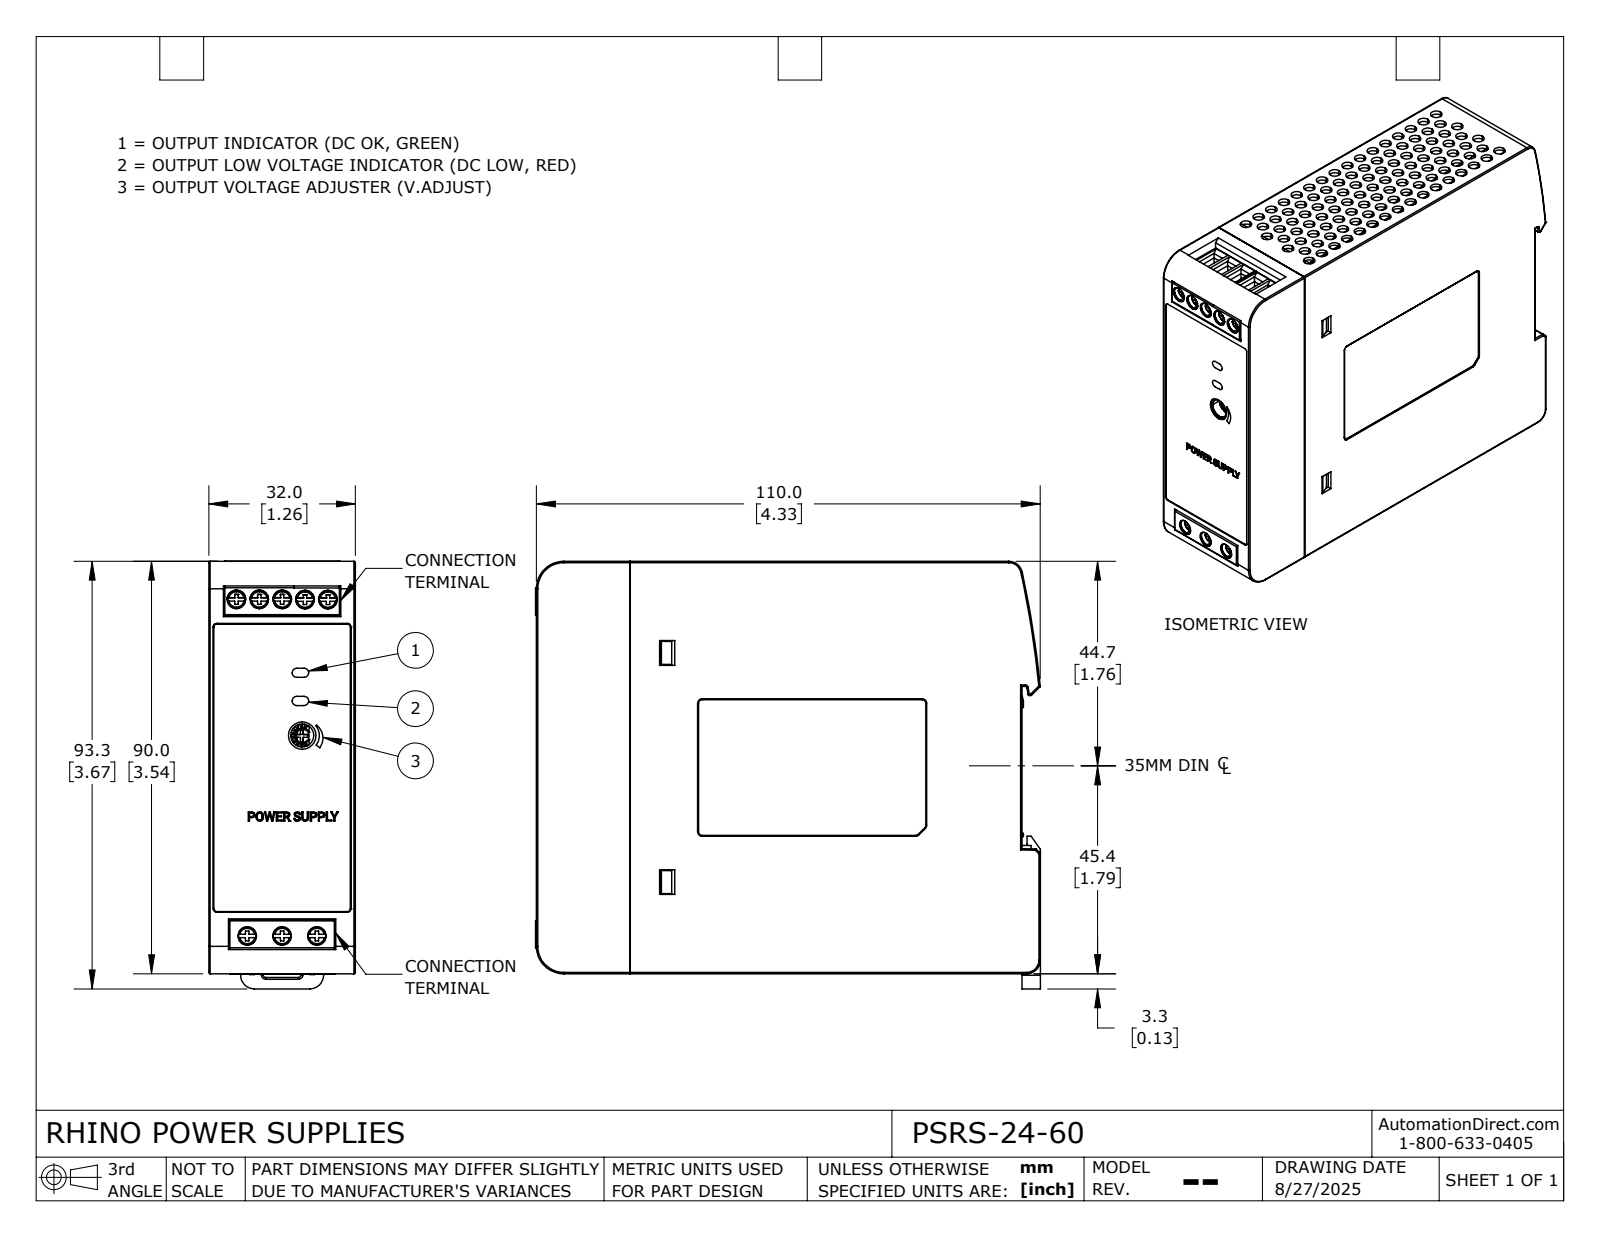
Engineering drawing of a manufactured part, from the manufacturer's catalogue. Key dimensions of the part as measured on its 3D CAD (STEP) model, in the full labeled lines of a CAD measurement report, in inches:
Part name (STEP PRODUCT): PSRS-24-60
STEP written by: SolidWorks 2024 (AUTOMOTIVE_DESIGN)
Units: inches
Bodies: 1 solid, 1700 faces (913 planar, 192 cylindrical, 595 other)
Overall size (bounding box): 4.339 × 3.673 × 1.26
Volume: 18.61 in³ · Surface area: 60.8 in²
Round holes (diameter × count): ⌀0.15 ×8, ⌀0.159 ×8, ⌀0.134 ×1, ⌀0.197 ×1
Round bosses / shafts (diameter × count): ⌀0.156 ×8, ⌀0.118 ×1
Partial cylindrical surfaces — rounded edges, fillets, slot ends (radius × count): R0.012 ×49, R0.039 ×12, R0.004 ×10, R0.02 ×7, R0.118 ×4, R0.098 ×3, R0.008 ×2, R0.024 ×2
Main face-to-face distances: 1.26, 3.543, 1.254, 0.039, 4.167, 3.504, 0.157, 4.325, 3.465, 0.079
Hole centre spacings: 0.197, 0.299, 0.393, 0.589, 1.727, 2.891, 0.196, 0.394
